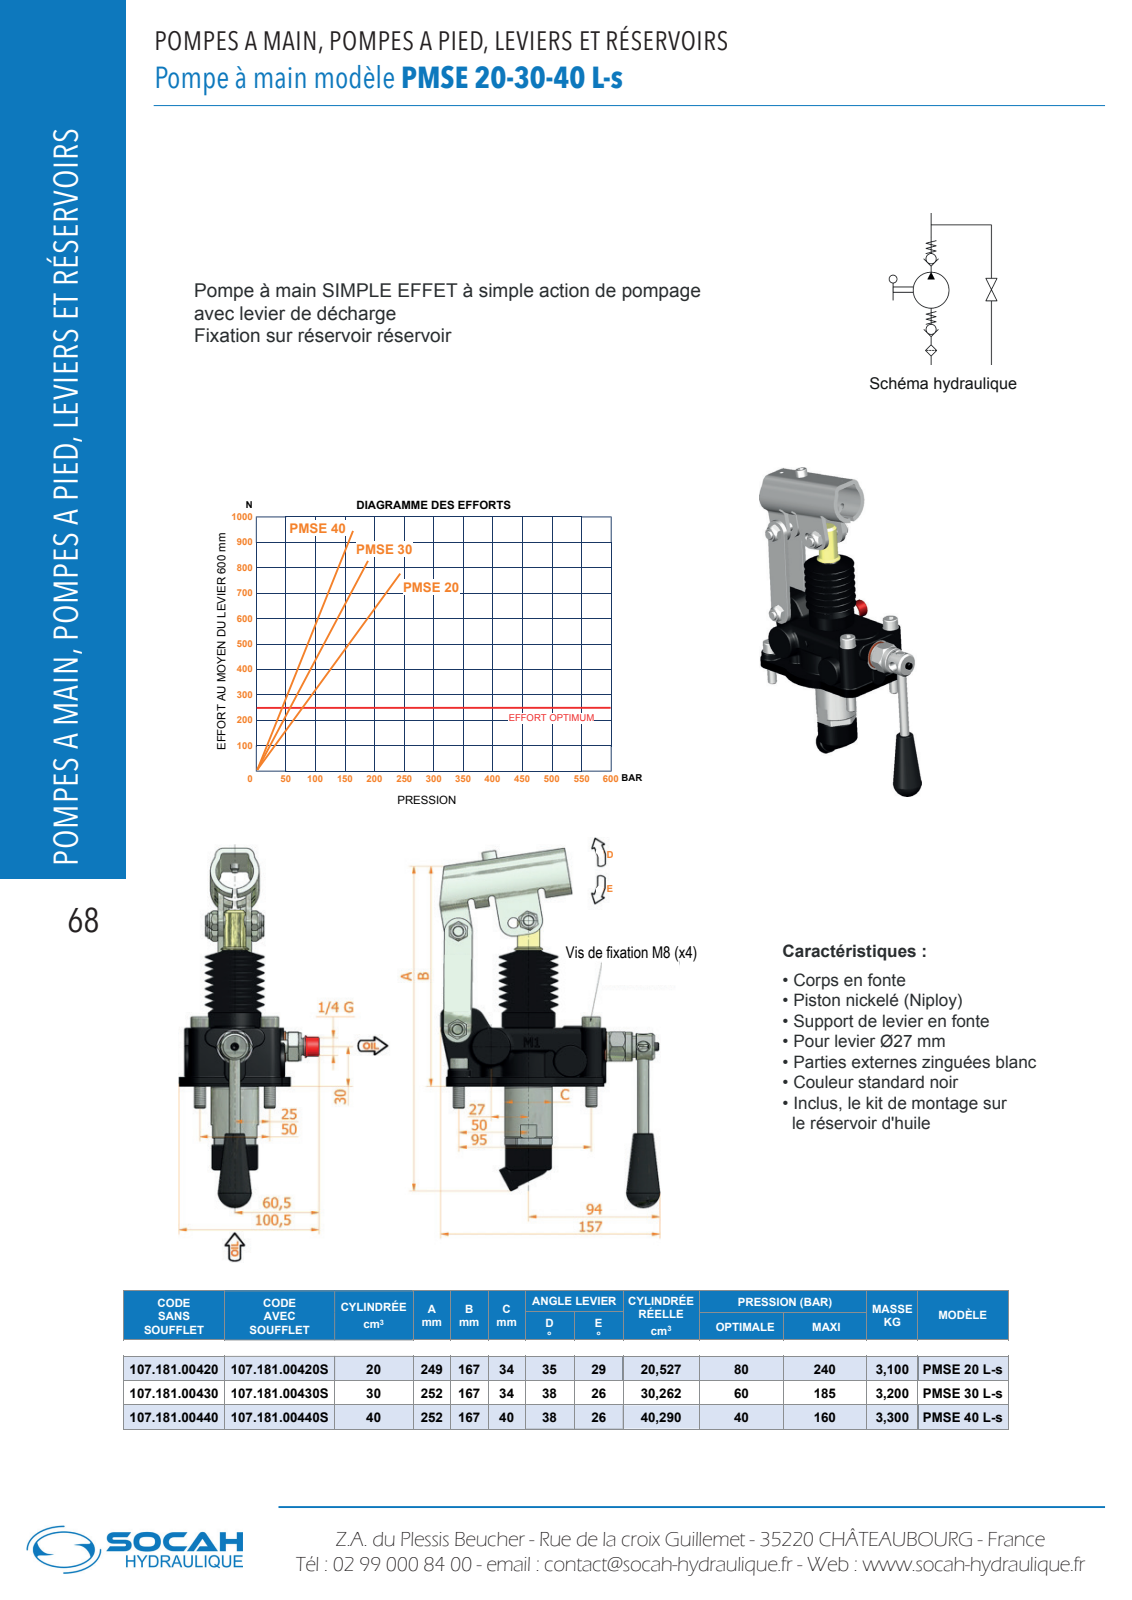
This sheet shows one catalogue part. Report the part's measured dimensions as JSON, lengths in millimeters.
{"part_name": "6067.0041.00", "step_written_by": "Autodesk Inventor 2013 (CONFIG_CONTROL_DESIGN)", "units": "millimeters", "bodies": {"solids": 1, "faces": 1490, "planar": 700, "cylindrical": 336, "other": 454}, "overall_size": [271.22, 157.92, 100.5], "volume_mm3": 314551, "surface_area_mm2": 146537, "round_holes": [[8, 4], [8.5, 4], [14, 4], [5, 2], [4, 1], [4.92, 1], [19, 1], [20.5, 1], [22, 1], [26, 1], [29, 1]], "round_bosses_or_shafts": [[8, 7], [13, 4], [12, 4], [20, 3], [11.05, 3], [6, 3], [23, 2], [16, 2]], "partial_cylinders_radius": [[1, 30], [0.2, 24], [0.1, 16], [5, 15], [2, 14], [3, 9], [8, 9], [0.36, 6]], "face_to_face_distances": [4, 2, 42, 20, 16, 37, 5, 44, 40, 7], "hole_center_spacings": [26.1, 44.84, 50, 51.48, 55.9, 91, 95, 107.35]}
